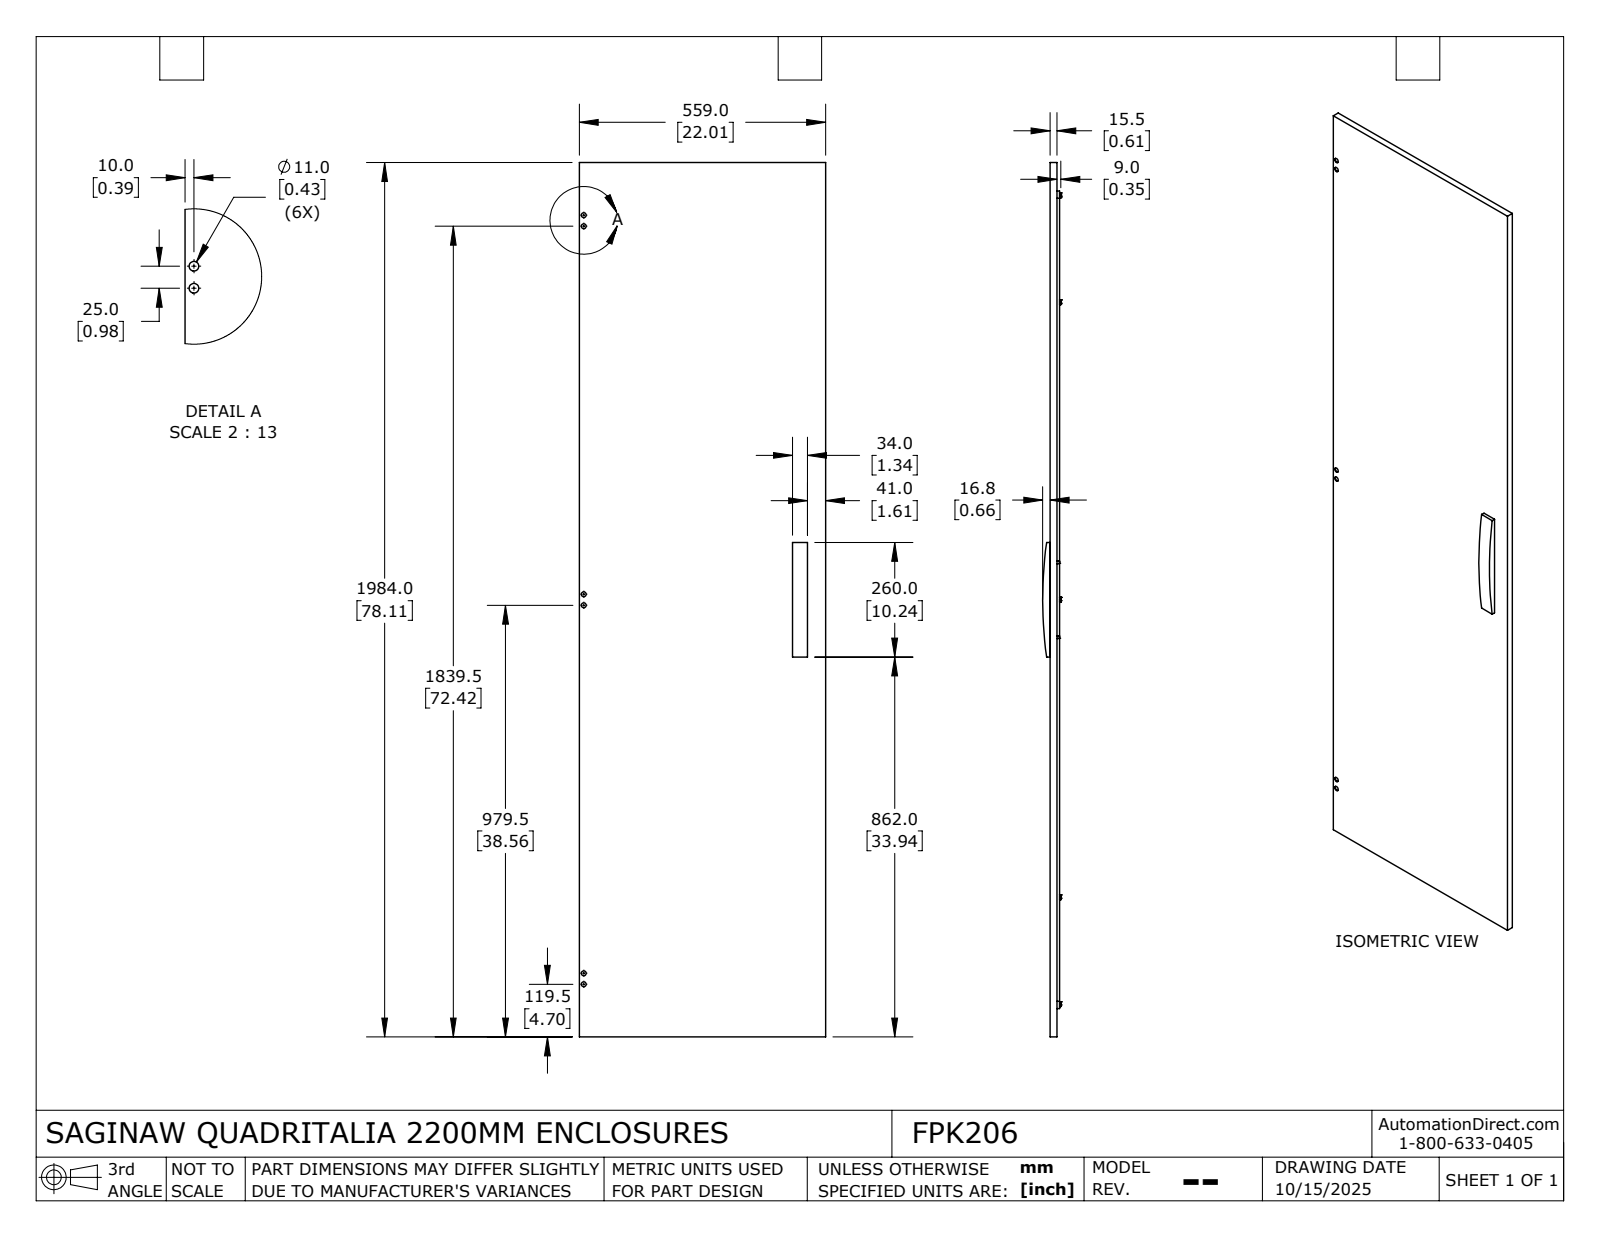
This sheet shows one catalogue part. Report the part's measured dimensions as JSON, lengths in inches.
{"part_name": "FPK206", "step_written_by": "SolidWorks 2024 (AUTOMOTIVE_DESIGN)", "units": "inches", "bodies": {"solids": 2, "faces": 566, "planar": 271, "cylindrical": 195, "other": 100}, "overall_size": [78.11, 22.008, 1.627], "volume_in3": 245.6, "surface_area_in2": 4044, "round_holes": [[0.167, 128], [0.194, 8], [0.354, 8], [0.433, 6]], "round_bosses_or_shafts": [[0.276, 4], [0.236, 4]], "partial_cylinders_radius": [[0.227, 8], [0.296, 4], [37.908, 1]], "face_to_face_distances": [0.059, 0.787, 0.846, 14.173, 21.949, 14.961, 13.386, 2.953, 19.055, 18.996], "hole_center_spacings": [0.984, 1.969, 2.953, 3.937, 4.921, 5.906, 6.89, 7.874]}
